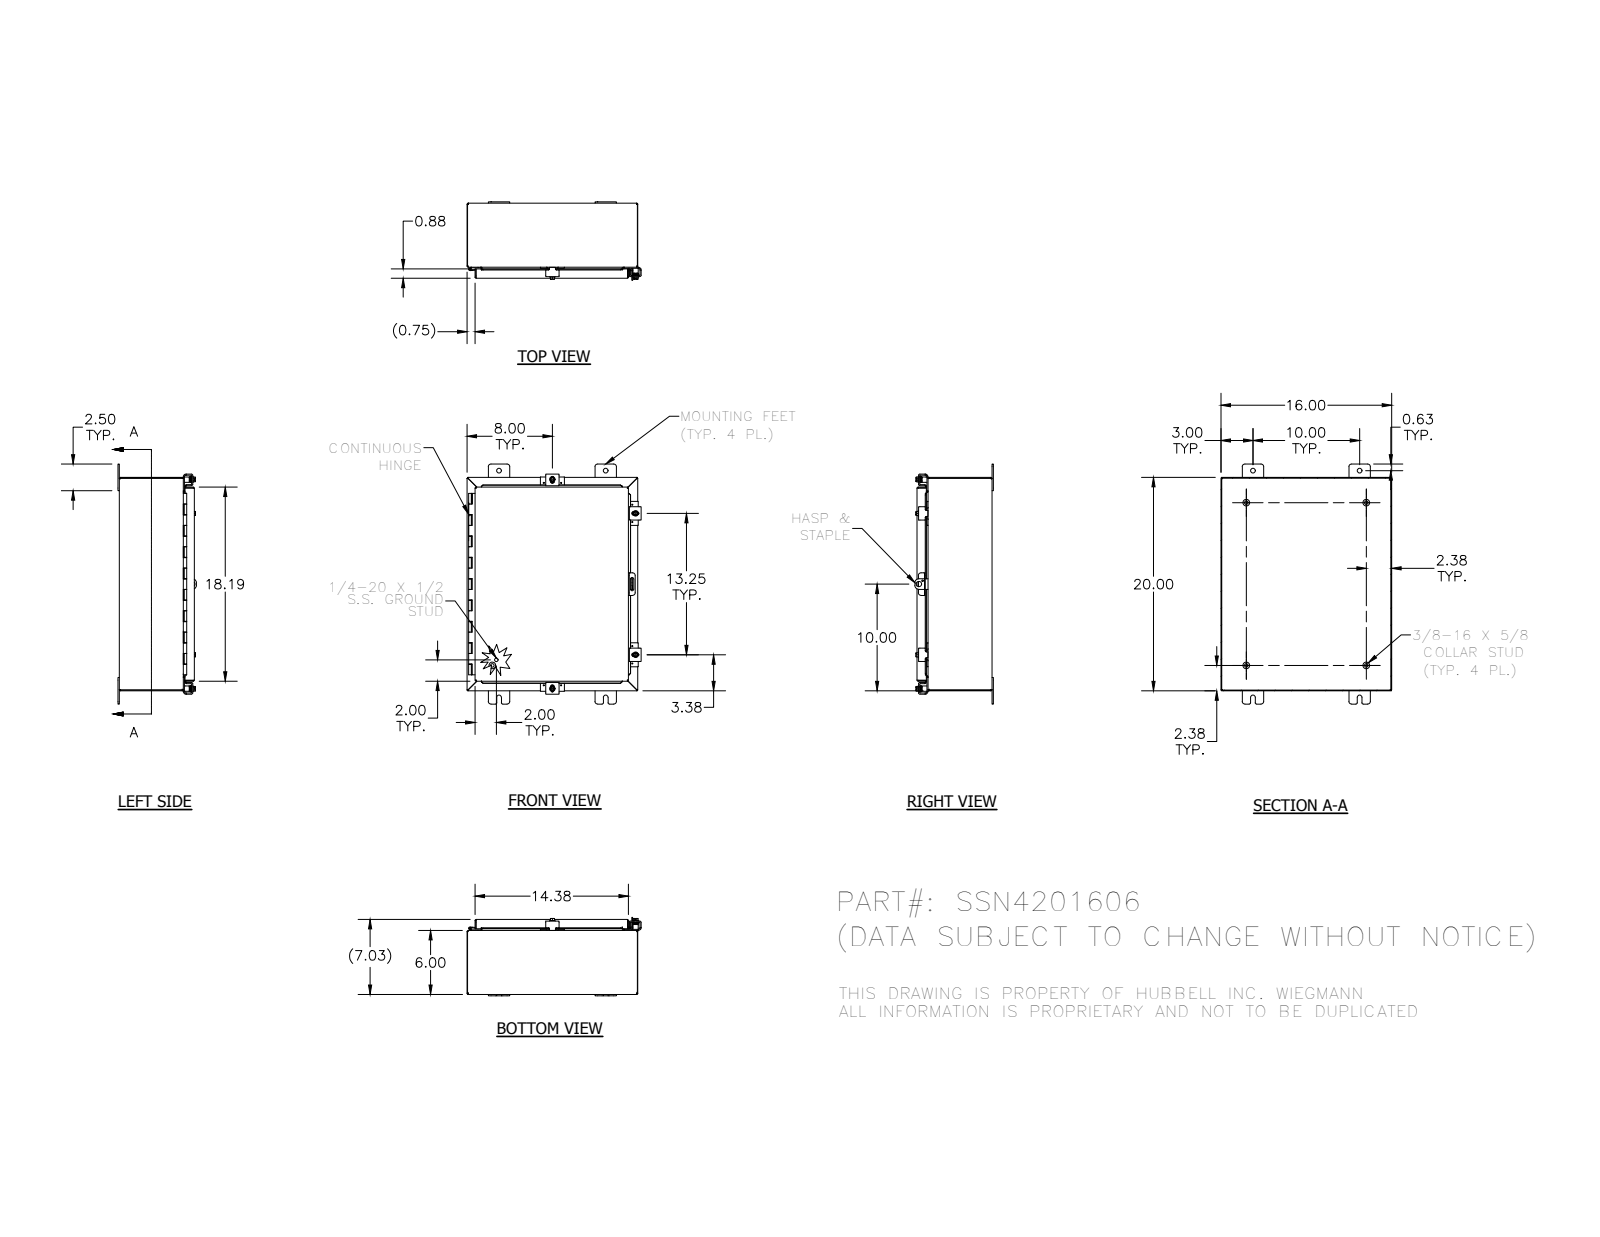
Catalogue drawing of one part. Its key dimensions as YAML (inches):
part_name: "SSN4201606; 34871_1; 32912_1; HFW30825-2_1 (+8 more)"
step_written_by: "SolidWorks 2014 (AUTOMOTIVE_DESIGN)"
units: inches
bodies: {solids: 37, faces: 1444, planar: 567, cylindrical: 632, other: 245}
overall_size: [22.5, 16.311, 7.355]
volume: 104
surface_area: 2705
round_holes:
  - {diameter: 0.11, count: 8}
  - {diameter: 0.211, count: 4}
  - {diameter: 0.281, count: 4}
  - {diameter: 0.3, count: 4}
  - {diameter: 0.438, count: 4}
  - {diameter: 0.125, count: 1}
  - {diameter: 0.156, count: 1}
  - {diameter: 0.5, count: 1}
round_bosses_or_shafts:
  - {diameter: 0.25, count: 6}
  - {diameter: 0.625, count: 4}
  - {diameter: 0.52, count: 4}
  - {diameter: 0.5, count: 4}
  - {diameter: 0.35, count: 4}
  - {diameter: 0.33, count: 4}
  - {diameter: 0.115, count: 2}
  - {diameter: 0.337, count: 1}
partial_cylinders:
  - {radius: 0.03, count: 49}
  - {radius: 0.125, count: 33}
  - {radius: 0.25, count: 29}
  - {radius: 0.031, count: 23}
  - {radius: 0.105, count: 23}
  - {radius: 0.062, count: 11}
  - {radius: 0.07, count: 8}
  - {radius: 0.141, count: 8}
face_to_face_distances: [0.074, 6.959, 6.885, 7.033, 15.926, 19.926, 5.926, 1.033, 15.852, 16]
hole_center_spacings: [0.876, 19.306, 13.25, 0.876, 1.625, 1.625, 4.189, 4.341]
